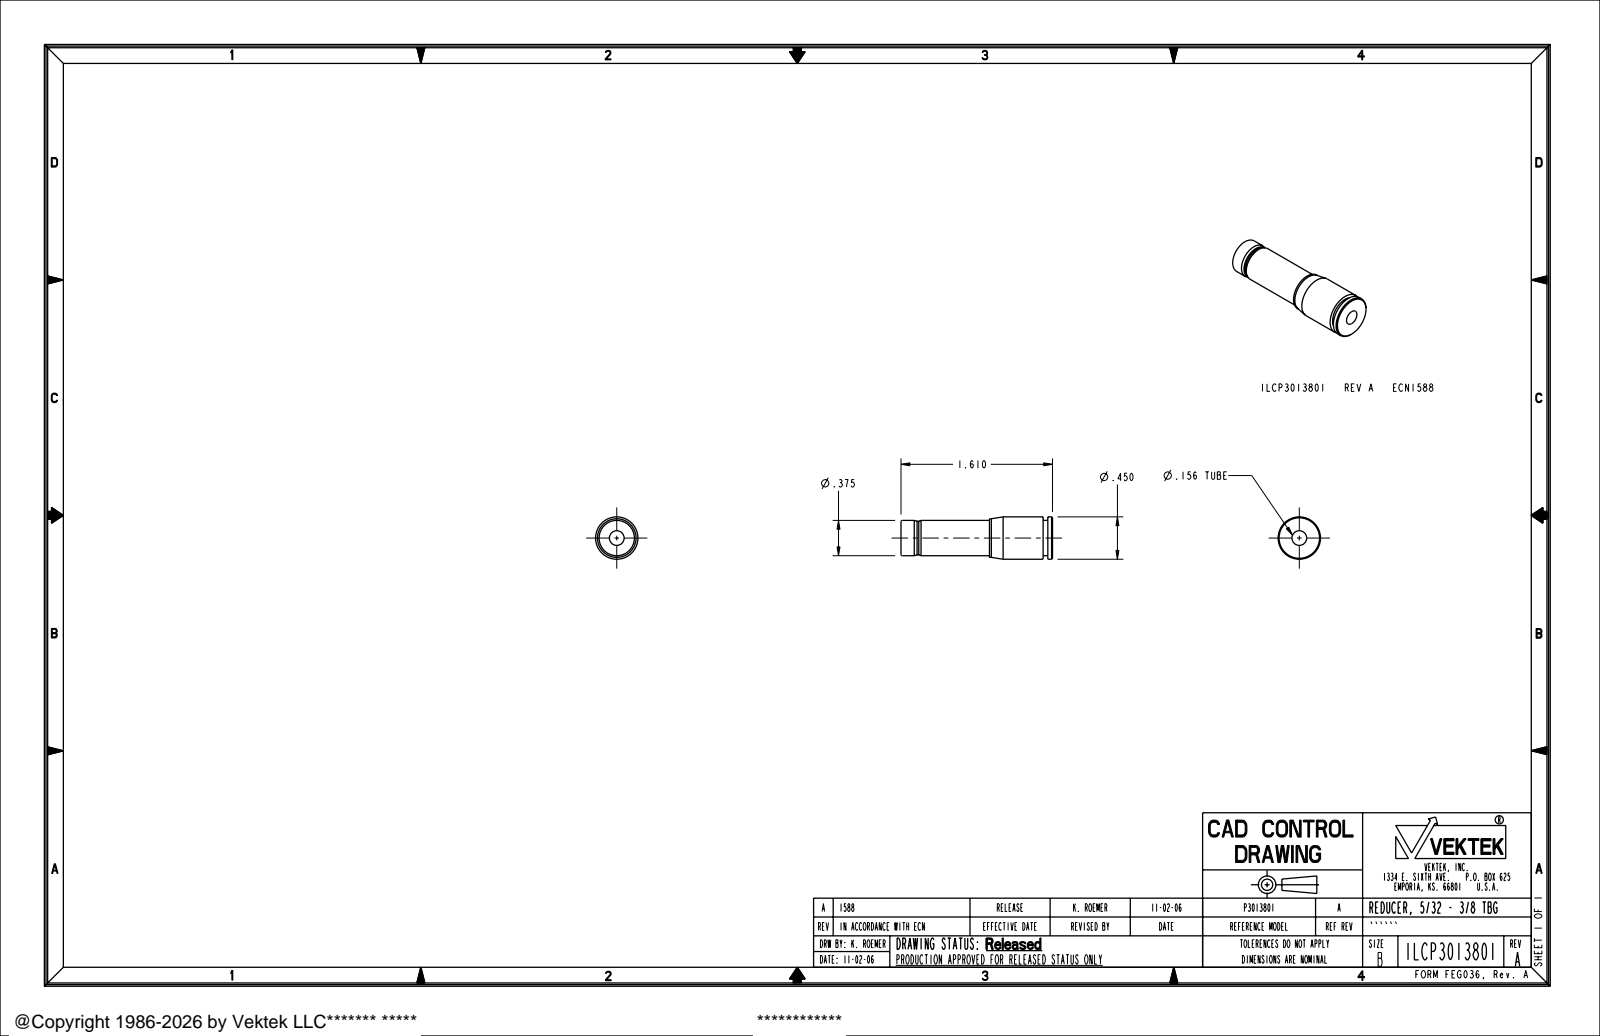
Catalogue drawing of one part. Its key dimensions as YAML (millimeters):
part_name: "ILCP3013801"
step_written_by: "PRO/ENGINEER BY PARAMETRIC TECHNOLOGY CORPORATION, 2005180 (AUTOMOTIVE_DESIGN_CC2)"
units: millimeters
bodies: {solids: 1, faces: 31, planar: 5, cylindrical: 16, other: 10}
overall_size: [40.9, 11.4, 11.4]
volume: 2850
surface_area: 2038
round_holes:
  - {diameter: 4, count: 1}
round_bosses_or_shafts:
  - {diameter: 11.4, count: 1}
  - {diameter: 10.4, count: 1}
  - {diameter: 9.5, count: 1}
  - {diameter: 9.1, count: 1}
face_to_face_distances: [1.3, 40.9, 38.4, 2.5, 39.6, 23.9, 14.5, 15.7, 17]
